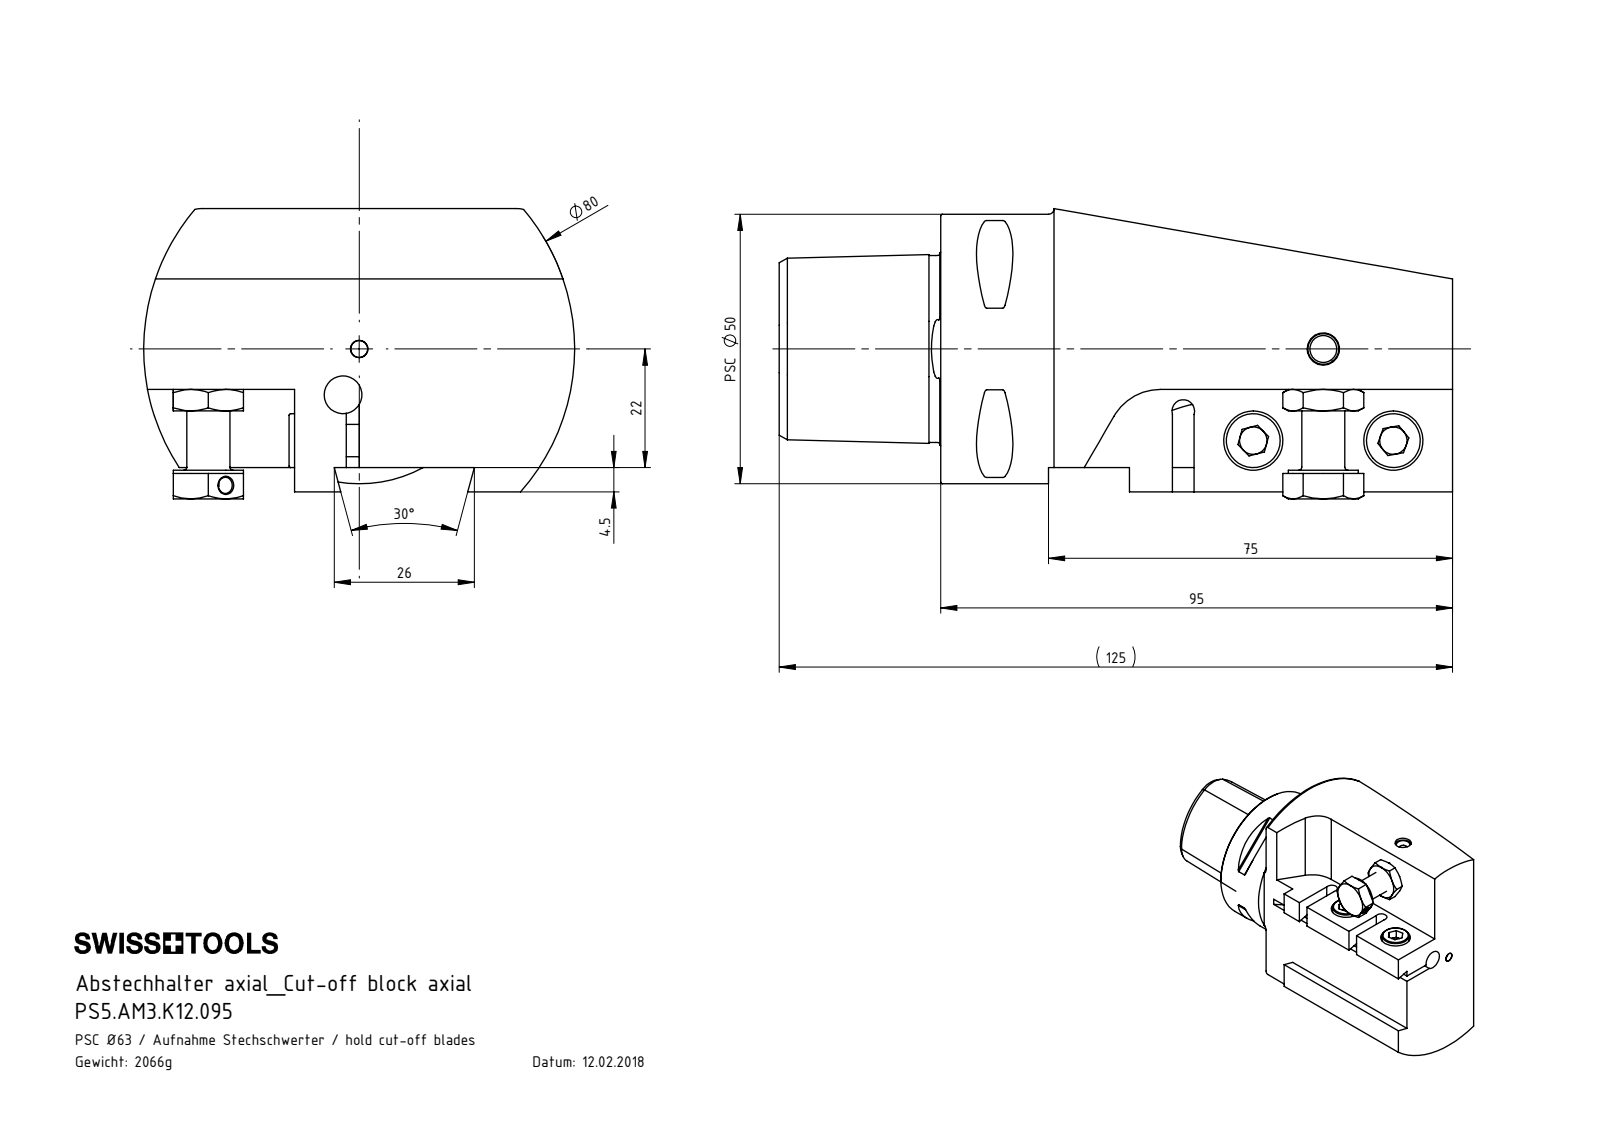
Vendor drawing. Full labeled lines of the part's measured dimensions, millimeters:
Part name (STEP PRODUCT): ISO 4762 - M6 x 16_PreviewCfg; ISO 4035 - M8_PreviewCfg; AM3-ER1.001.020_PreviewCfg; PS5-AM3.K12.095_A (+2 more)
STEP written by: SolidWorks 2017 (AUTOMOTIVE_DESIGN)
Units: millimetres
Bodies: 7 solids, 257 faces (103 planar, 48 cylindrical, 106 other)
Overall size (bounding box): 125 × 80 × 53.85
Volume: 264 380 mm³ · Surface area: 42 519 mm²
Round holes (diameter × count): ⌀5 ×3, ⌀6.4 ×3, ⌀4 ×2, ⌀7 ×2, ⌀11 ×2, ⌀3 ×1, ⌀3.15 ×1, ⌀6.1 ×1, ⌀6.5 ×1, ⌀8.5 ×1, ⌀14.5 ×1, ⌀21 ×1
Round bosses / shafts (diameter × count): ⌀6 ×3, ⌀10 ×2, ⌀50 ×1, ⌀13 ×1, ⌀8 ×1
Partial cylindrical surfaces — rounded edges, fillets, slot ends (radius × count): R0.5 ×8, R2.1 ×2, R4 ×1, R10 ×1, R40 ×1, R52 ×1
Main face-to-face distances: 14.5, 74, 19, 4.5, 12, 21, 95, 30, 26, 2.4
Hole centre spacings: 21.4, 26, 73.98, 9.01, 49.04, 59, 85, 99.46
